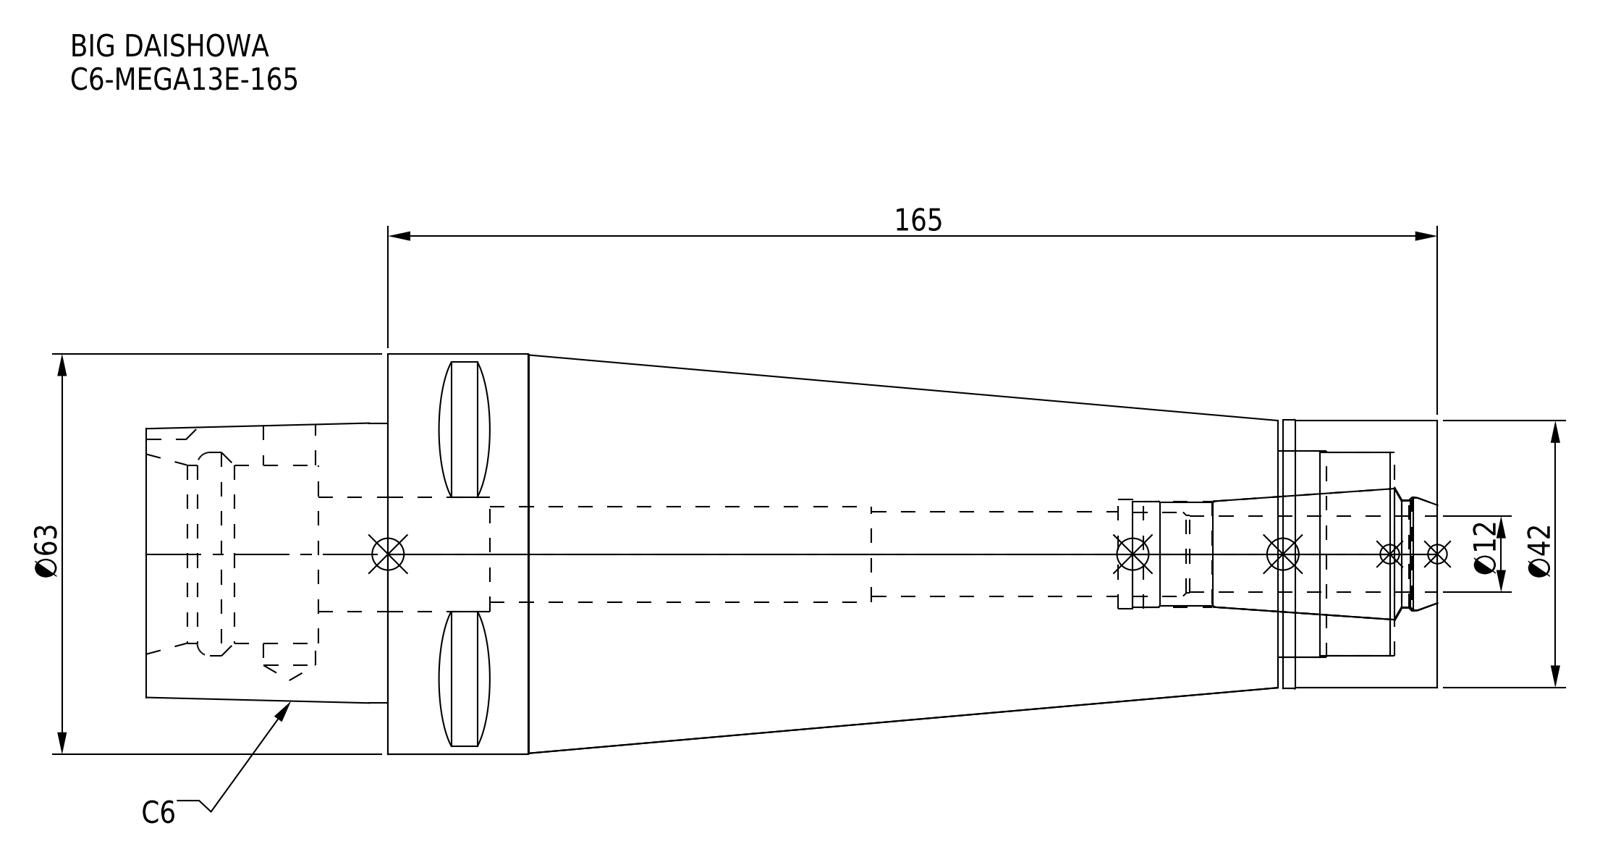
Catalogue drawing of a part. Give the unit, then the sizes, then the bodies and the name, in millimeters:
Units: millimetres
Overall size (bounding box): 203 × 63 × 63
Round holes (diameter × count): ⌀8.1 ×1, ⌀13.3 ×1, ⌀15 ×1, ⌀16.6 ×1, ⌀17 ×1, ⌀17.2 ×1, ⌀17.9 ×1, ⌀18 ×1, ⌀28 ×1, ⌀32 ×1, ⌀32.5 ×1
Round bosses / shafts (diameter × count): ⌀63 ×1, ⌀42.3 ×1, ⌀42 ×1
Partial cylindrical surfaces — rounded edges, fillets, slot ends (radius × count): R5 ×1
Main face-to-face distances: 165, 25.1, 24.3, 140.7, 0.8, 139.9, 157.5, 203, 178.7, 177.9
Volume: 358 646 mm³ · Surface area: 53 868 mm²
Bodies: 2 solids, 100 faces (37 planar, 39 cylindrical, 24 other)
Part name (STEP PRODUCT): C6-MEGA13E-165-120_ASM.stp; DXF_TEMP_ASSY_ASM_4_ASM.stp; C6-MEGA13E-165-120.stp; C6-MEGA13E-165_1.stp (+3 more)
STEP written by: SolidWorks 2019 (CONFIG_CONTROL_DESIGN)
